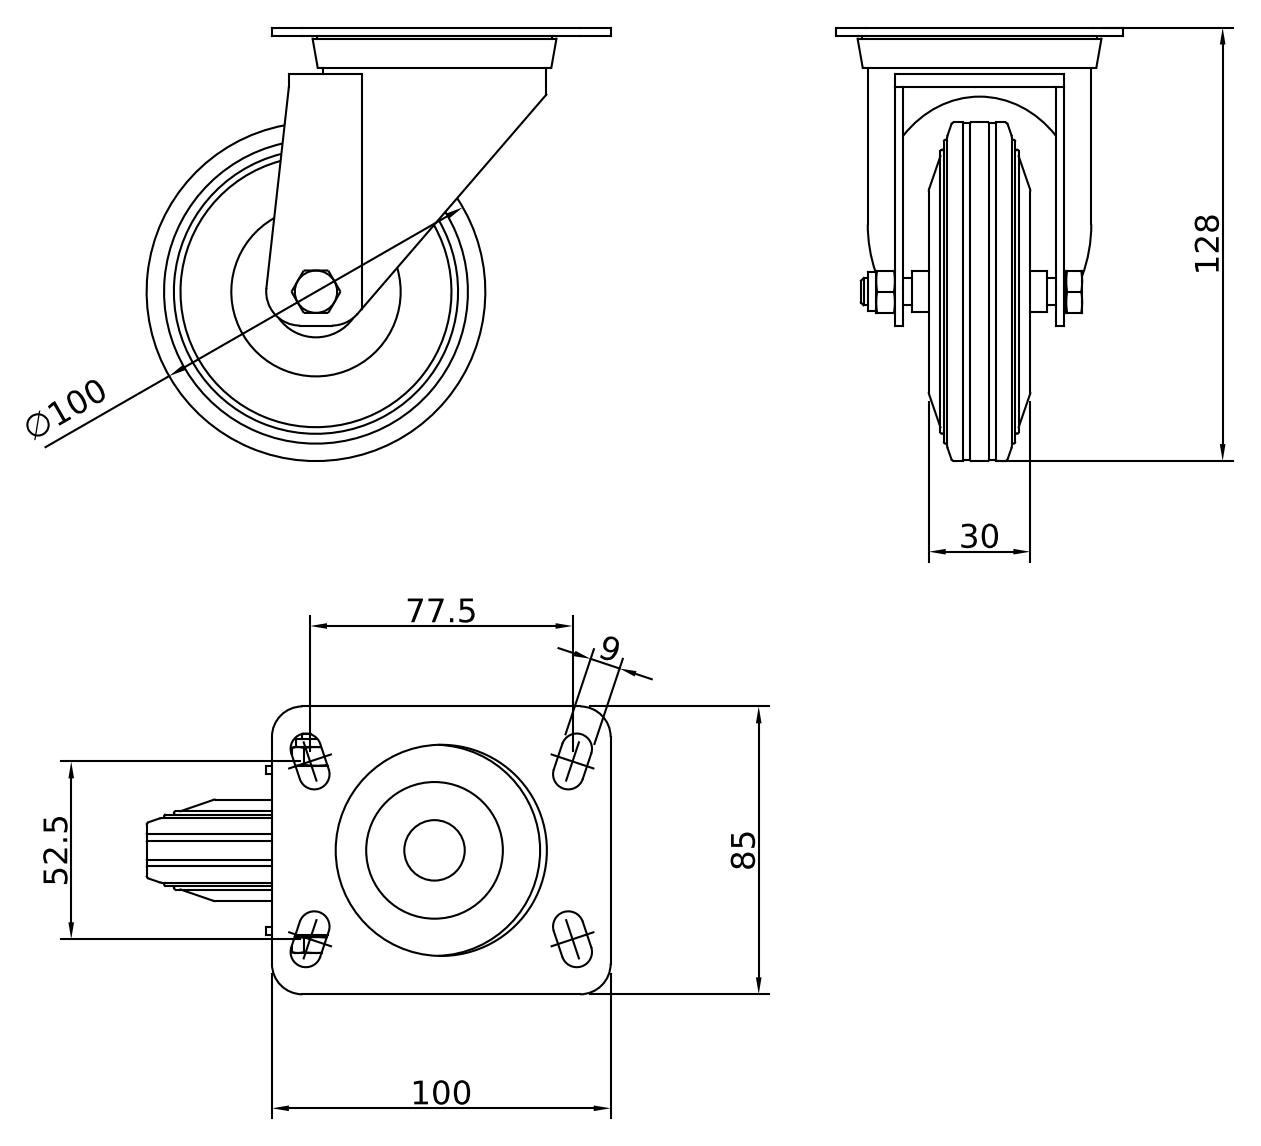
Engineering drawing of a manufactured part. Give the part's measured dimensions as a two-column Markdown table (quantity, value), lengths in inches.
| quantity | value |
| --- | --- |
| part name | CRUST0000199; 440000025845; 440000025844; 440000025843 |
| STEP written by | Autodesk Inventor 2022 (AUTOMOTIVE_DESIGN) |
| units | inches |
| bodies | 3 solids, 168 faces (67 planar, 37 cylindrical, 64 other) |
| overall size | 5.394 × 5.039 × 3.346 |
| volume | 15.69 in³ |
| surface area | 108.8 in² |
| round holes (diameter × count) | 0.354 × 1, 0.472 × 1, 1.589 × 1, 2.402 × 1, 2.455 × 1 |
| round bosses / shafts (diameter × count) | 3.937 × 1, 3.917 × 1, 2.74 × 1, 2.598 × 1, 0.458 × 1, 0.315 × 1 |
| partial cylindrical surfaces (radius × count) | 0.177 × 8, 0.354 × 4, 0.394 × 2, 1.228 × 1 |
| main face-to-face distances | 0.098, 1.87, 0.551, 0.453, 1.575, 0.394, 0.295, 1.476, 1.772, 1.969 |
| hole center spacings | 0.079 |
